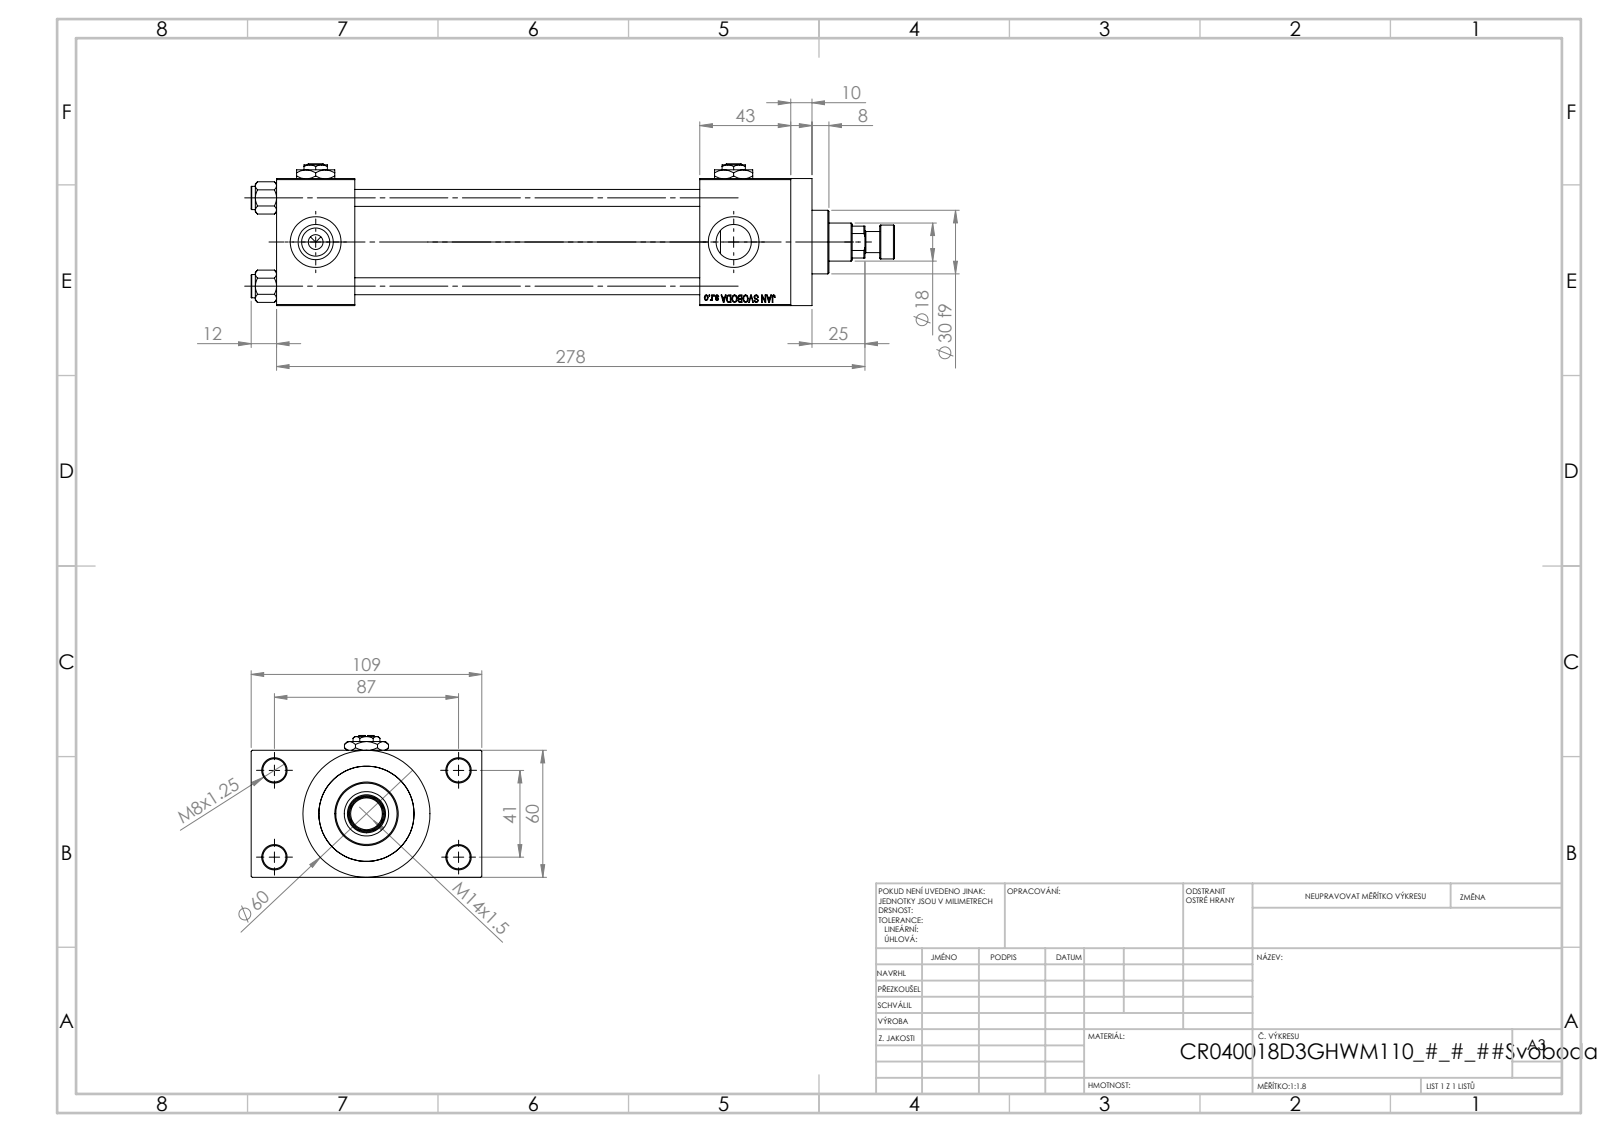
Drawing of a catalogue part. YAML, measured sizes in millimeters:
part_name: "V215CR_VCP_D; V215CR_ROD_END_W; V215_VC_A; Zatka_pro_OIL_PORT (+3 more)"
step_written_by: "SolidWorks 2019 (CONFIG_CONTROL_DESIGN)"
units: millimeters
bodies: {solids: 14, faces: 1218, planar: 549, cylindrical: 103, other: 566}
overall_size: [304, 109, 67]
volume: 602677
surface_area: 171030
round_holes:
  - {diameter: 8, count: 4}
  - {diameter: 11, count: 4}
  - {diameter: 16.66, count: 4}
  - {diameter: 24, count: 4}
  - {diameter: 7, count: 3}
  - {diameter: 8.5, count: 1}
  - {diameter: 18, count: 1}
  - {diameter: 21, count: 1}
  - {diameter: 31, count: 1}
  - {diameter: 40, count: 1}
  - {diameter: 45, count: 1}
round_bosses_or_shafts:
  - {diameter: 11, count: 4}
  - {diameter: 60, count: 1}
  - {diameter: 46, count: 1}
  - {diameter: 30, count: 1}
  - {diameter: 16, count: 1}
  - {diameter: 10, count: 1}
partial_cylinders:
  - {radius: 8.5, count: 1}
face_to_face_distances: [60, 24.5, 163, 84.5, 37, 200, 43, 243, 206, 10]
hole_center_spacings: [22.65, 29.49, 41.7, 47.15, 48.09, 64.35, 76.49, 41]
